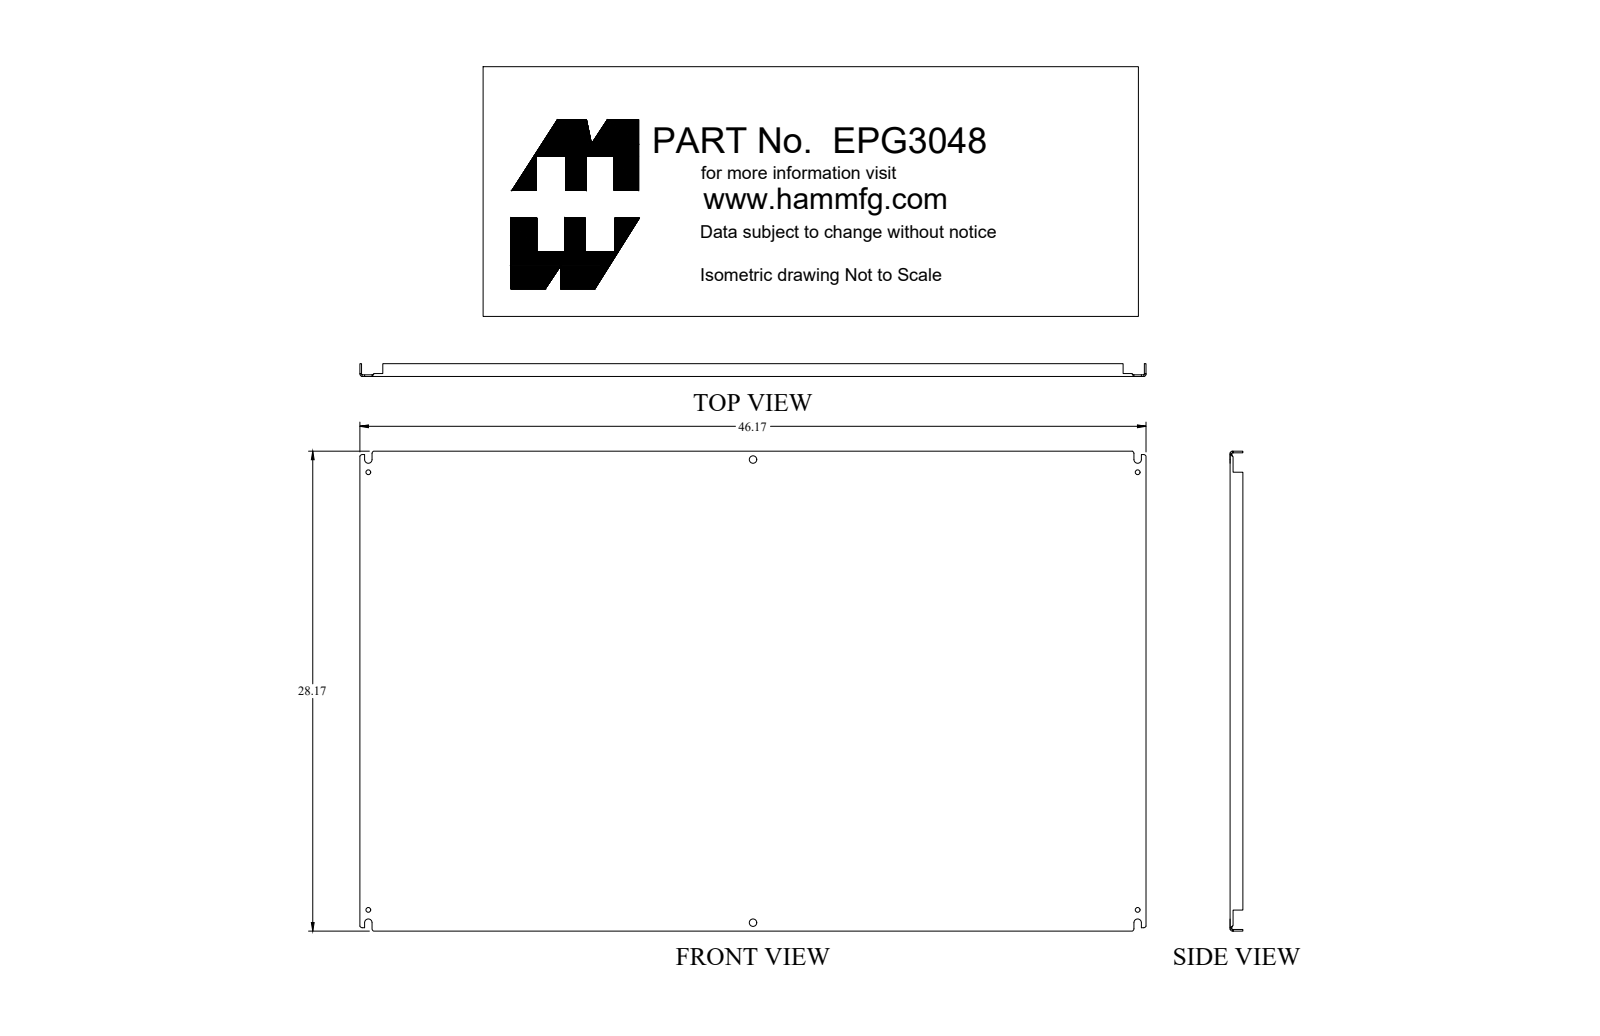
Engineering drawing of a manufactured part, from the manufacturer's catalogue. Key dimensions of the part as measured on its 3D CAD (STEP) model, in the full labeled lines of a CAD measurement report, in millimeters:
Part name (STEP PRODUCT): EPG3048
STEP written by: SolidWorks 2018 (AUTOMOTIVE_DESIGN)
Units: millimetres
Bodies: 1 solid, 132 faces (74 planar, 42 cylindrical, 16 other)
Overall size (bounding box): 1172.7 × 715.5 × 19.1
Volume: 2 153 000 mm³ · Surface area: 1 795 000 mm²
Round holes (diameter × count): ⌀7.1 ×4, ⌀11.1 ×2
Partial cylindrical surfaces — rounded edges, fillets, slot ends (radius × count): R1.2 ×4, R1.6 ×4, R3.6 ×4, R5.6 ×4
Main face-to-face distances: 2.4, 713.1, 1170.3, 715.5, 710.7, 1167.9, 1172.7, 19.1, 16.6, 4.3
Hole centre spacings: 574.2, 883.4, 652.5, 1147.8, 1320.3, 690.6
